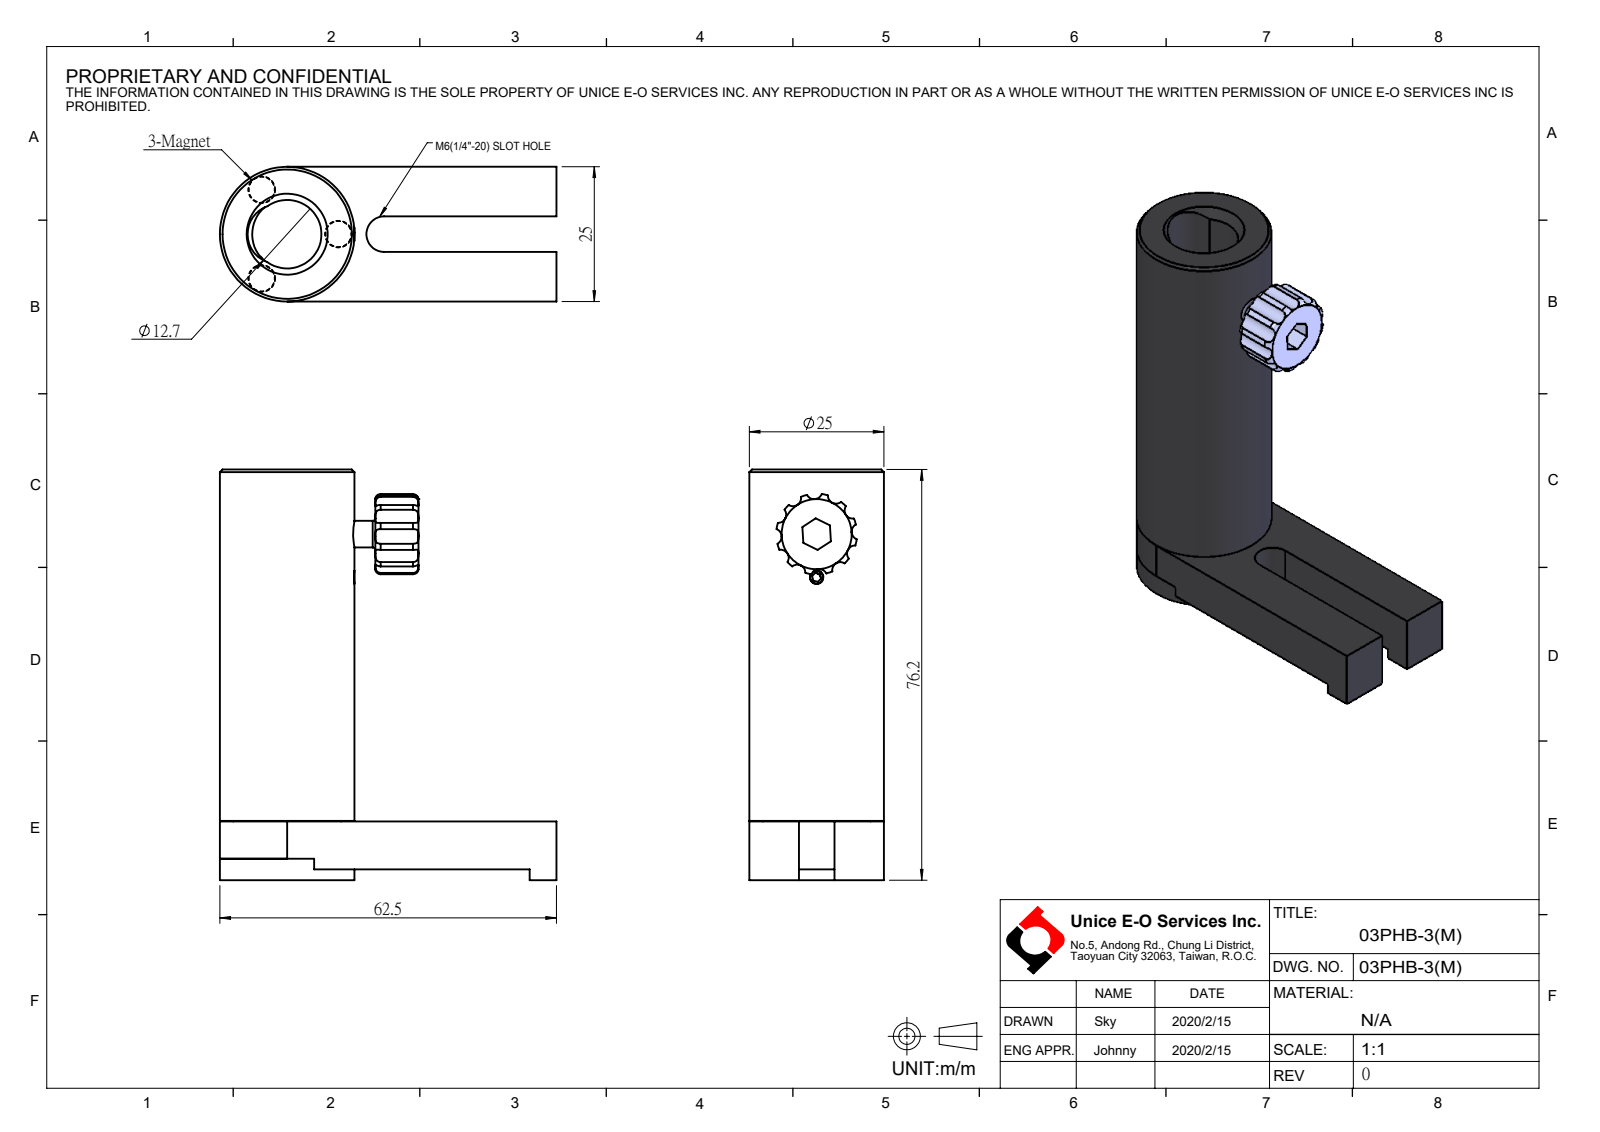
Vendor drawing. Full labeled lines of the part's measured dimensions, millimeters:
Part name (STEP PRODUCT): 03PHB-3(M)
STEP written by: SolidWorks 2016 (AUTOMOTIVE_DESIGN)
Units: millimetres
Bodies: 0 solids, 122 faces (35 planar, 49 cylindrical, 38 other)
Overall size (bounding box): 76.2 × 62.5 × 25
Round holes (diameter × count): ⌀5 ×3, ⌀13 ×1
Round bosses / shafts (diameter × count): ⌀25 ×1, ⌀4.94 ×1
Partial cylindrical surfaces — rounded edges, fillets, slot ends (radius × count): R1.5 ×12, R3.3 ×1, R5.5 ×1, R6.36 ×1, R7.5 ×1
Main face-to-face distances: 2, 8.9, 9.2, 15.8, 10.9, 25, 4, 6.9, 6.6, 76.2
Hole centre spacings: 9.5, 16.46
